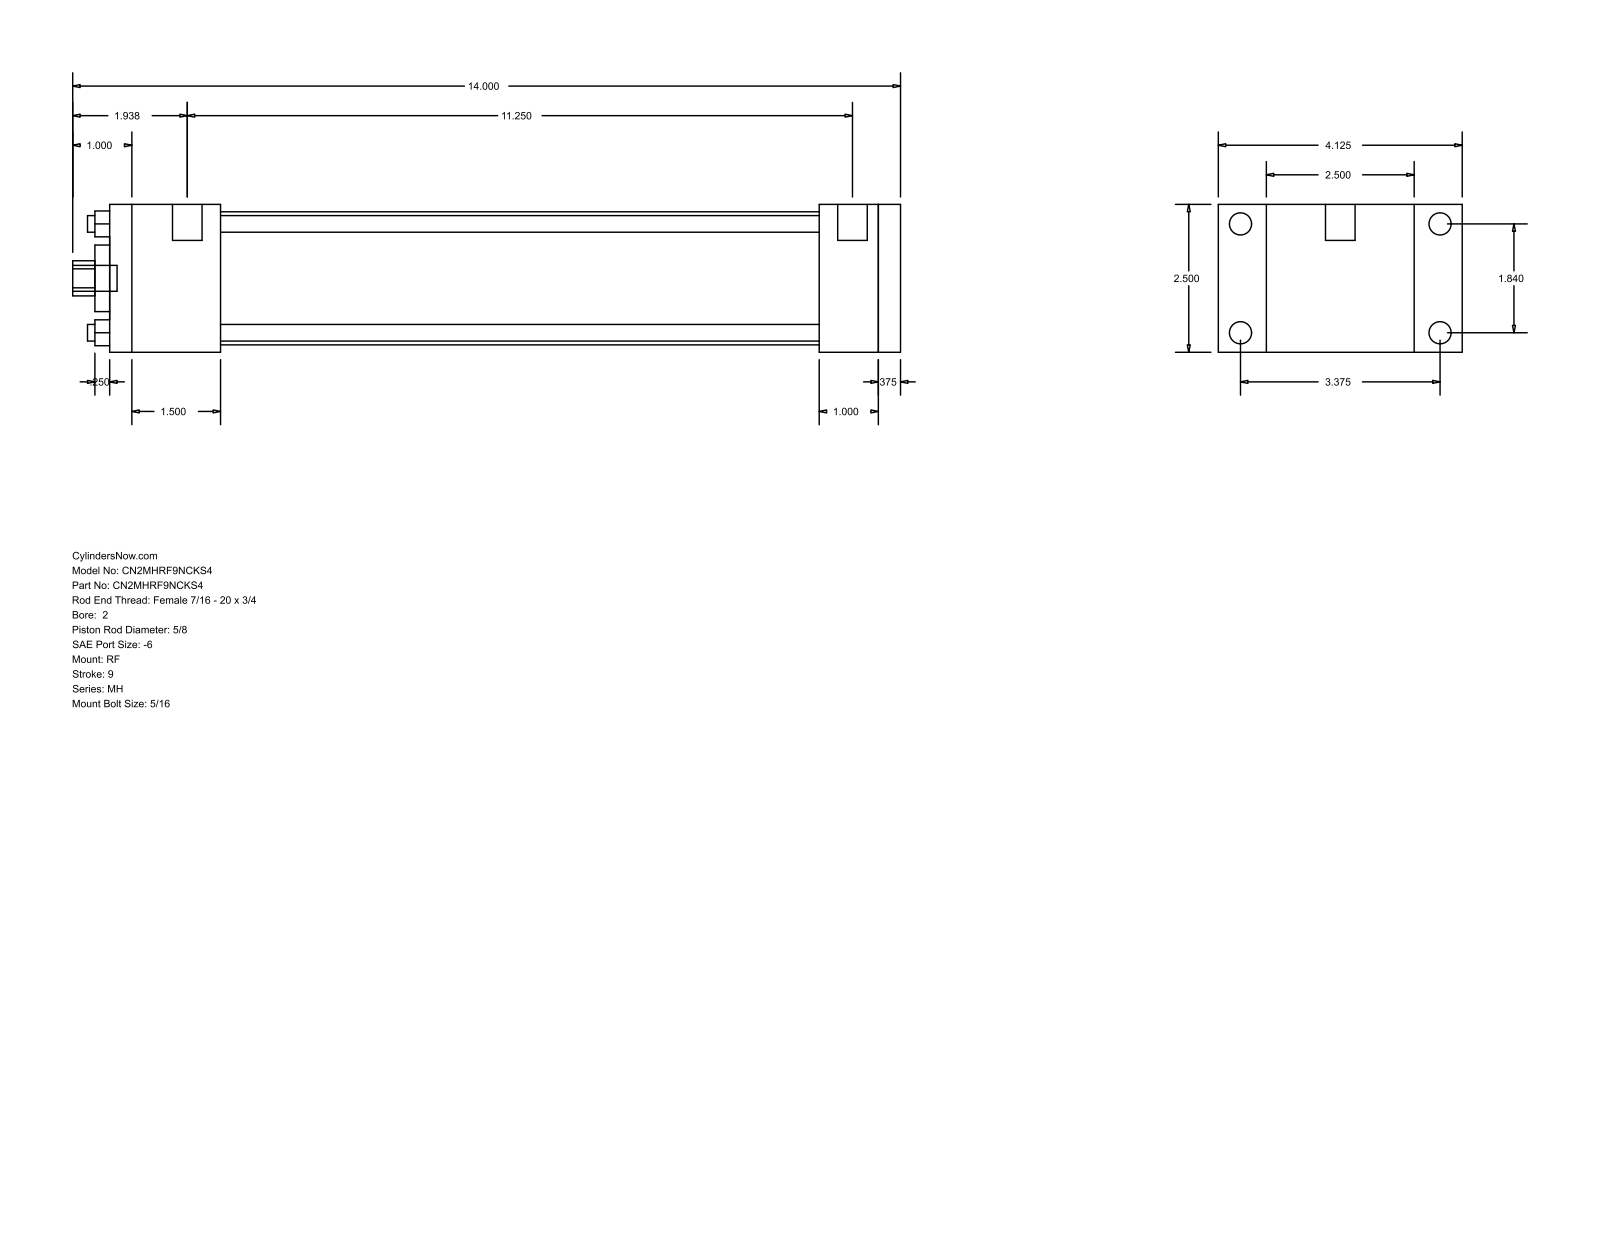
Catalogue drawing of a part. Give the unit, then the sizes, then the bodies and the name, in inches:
Units: inches
Overall size (bounding box): 14 × 4.125 × 2.5
Round holes (diameter × count): ⌀0.281 ×4, ⌀0.625 ×1, ⌀1.125 ×1, ⌀2.25 ×1
Round bosses / shafts (diameter × count): ⌀0.375 ×4, ⌀0.219 ×4, ⌀0.5 ×2, ⌀0.437 ×1
Partial cylindrical surfaces — rounded edges, fillets, slot ends (radius × count): R0.297 ×1
Main face-to-face distances: 2.5, 13.375, 0.375, 13, 1.875, 12, 10.125, 11.125, 11.5, 1
Hole centre spacings: 1.301, 1.84, 2.602
Bodies: 0 solids, 92 faces (64 planar, 28 cylindrical, 0 other)
Part name (STEP PRODUCT): MH_RF__0200_0.625
STEP written by: GSSL Pune (CONFIG_CONTROL_DESIGN)
